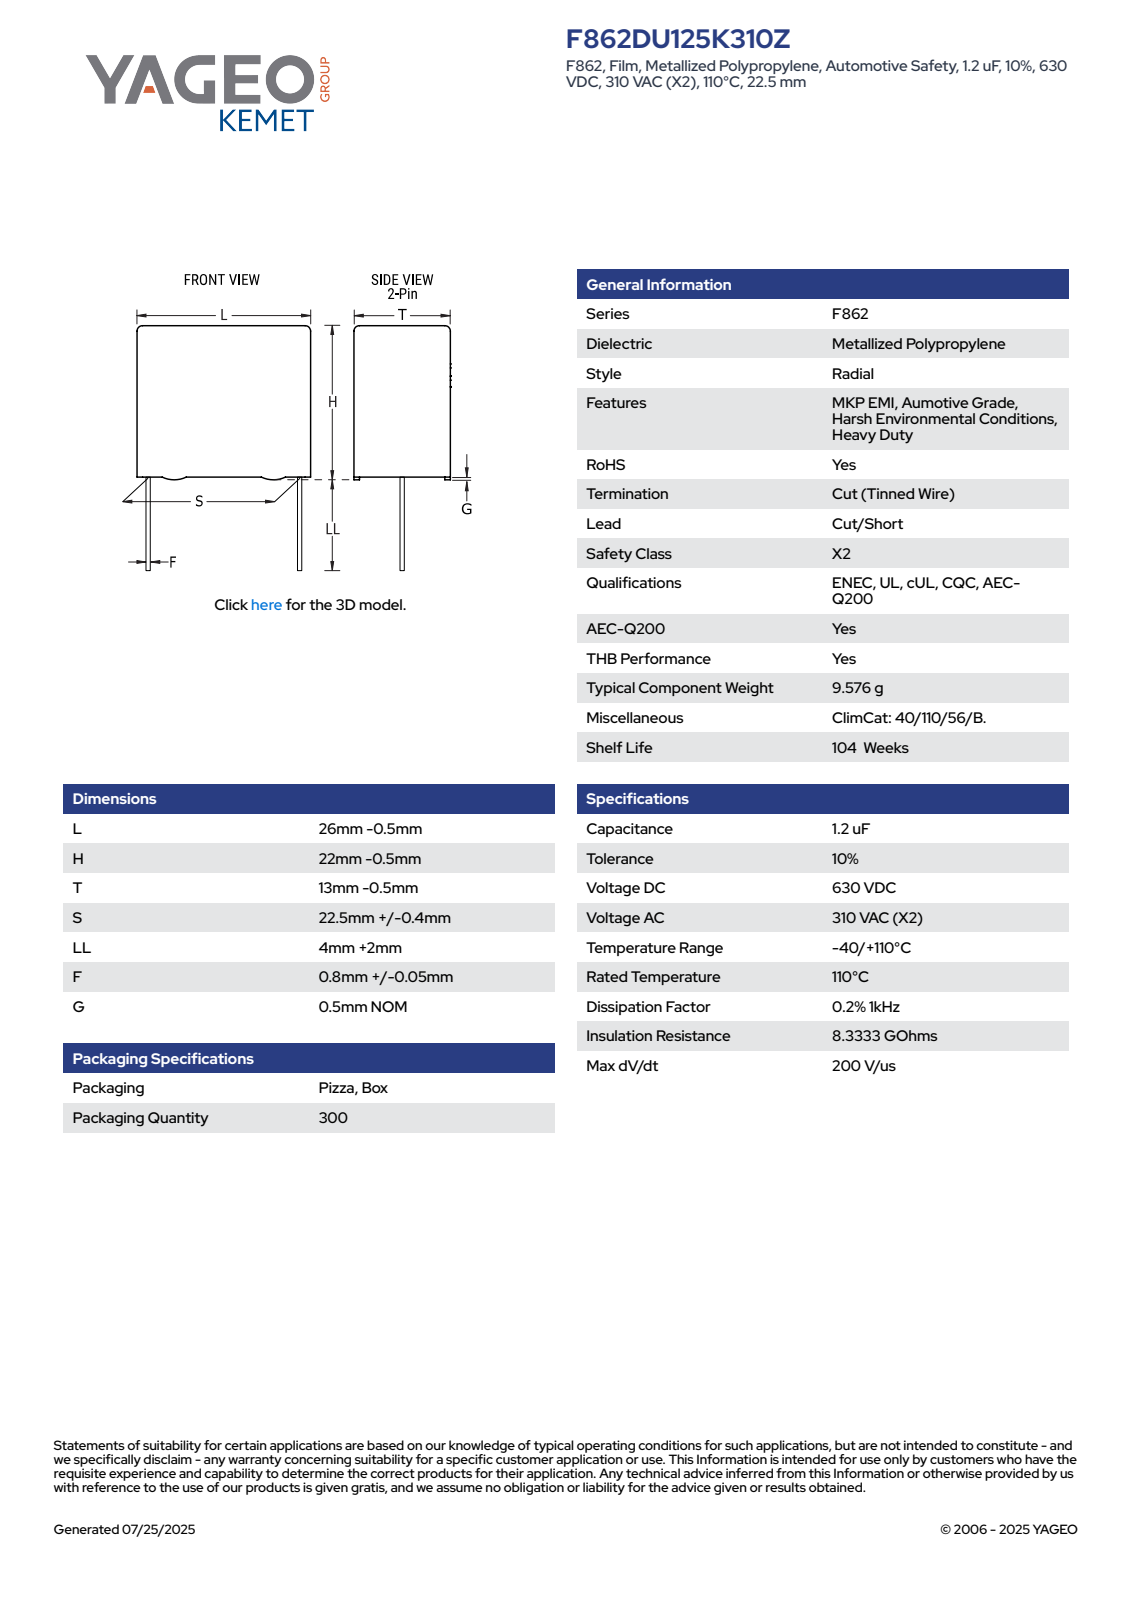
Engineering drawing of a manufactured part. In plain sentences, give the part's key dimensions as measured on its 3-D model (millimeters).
The part is named "CFR_RBG_26X22X13_L25.5H21.5T12.5S22.5LL6F0.85G0.5". Its 3-D file was written by "SolidWorks 2014 (AUTOMOTIVE_DESIGN)". It is 4 solids with 89 faces: 81 planar, 8 cylindrical and 0 other. Overall it measures 27.5 by 25.5 by 12.51 millimeters. Its volume is 6 703 cubic millimeters and its surface area 2 340 square millimeters. Round bosses or shafts: 2 of diameter 0.85. Partial cylindrical surfaces (rounded edges, fillets, slot ends): 4 of radius 0.5. The main face-to-face distances are 12.5, 21, 25.5, 12.51, 0.5, 21.5, 0.71, 11.79, 0.72, 11.08.
